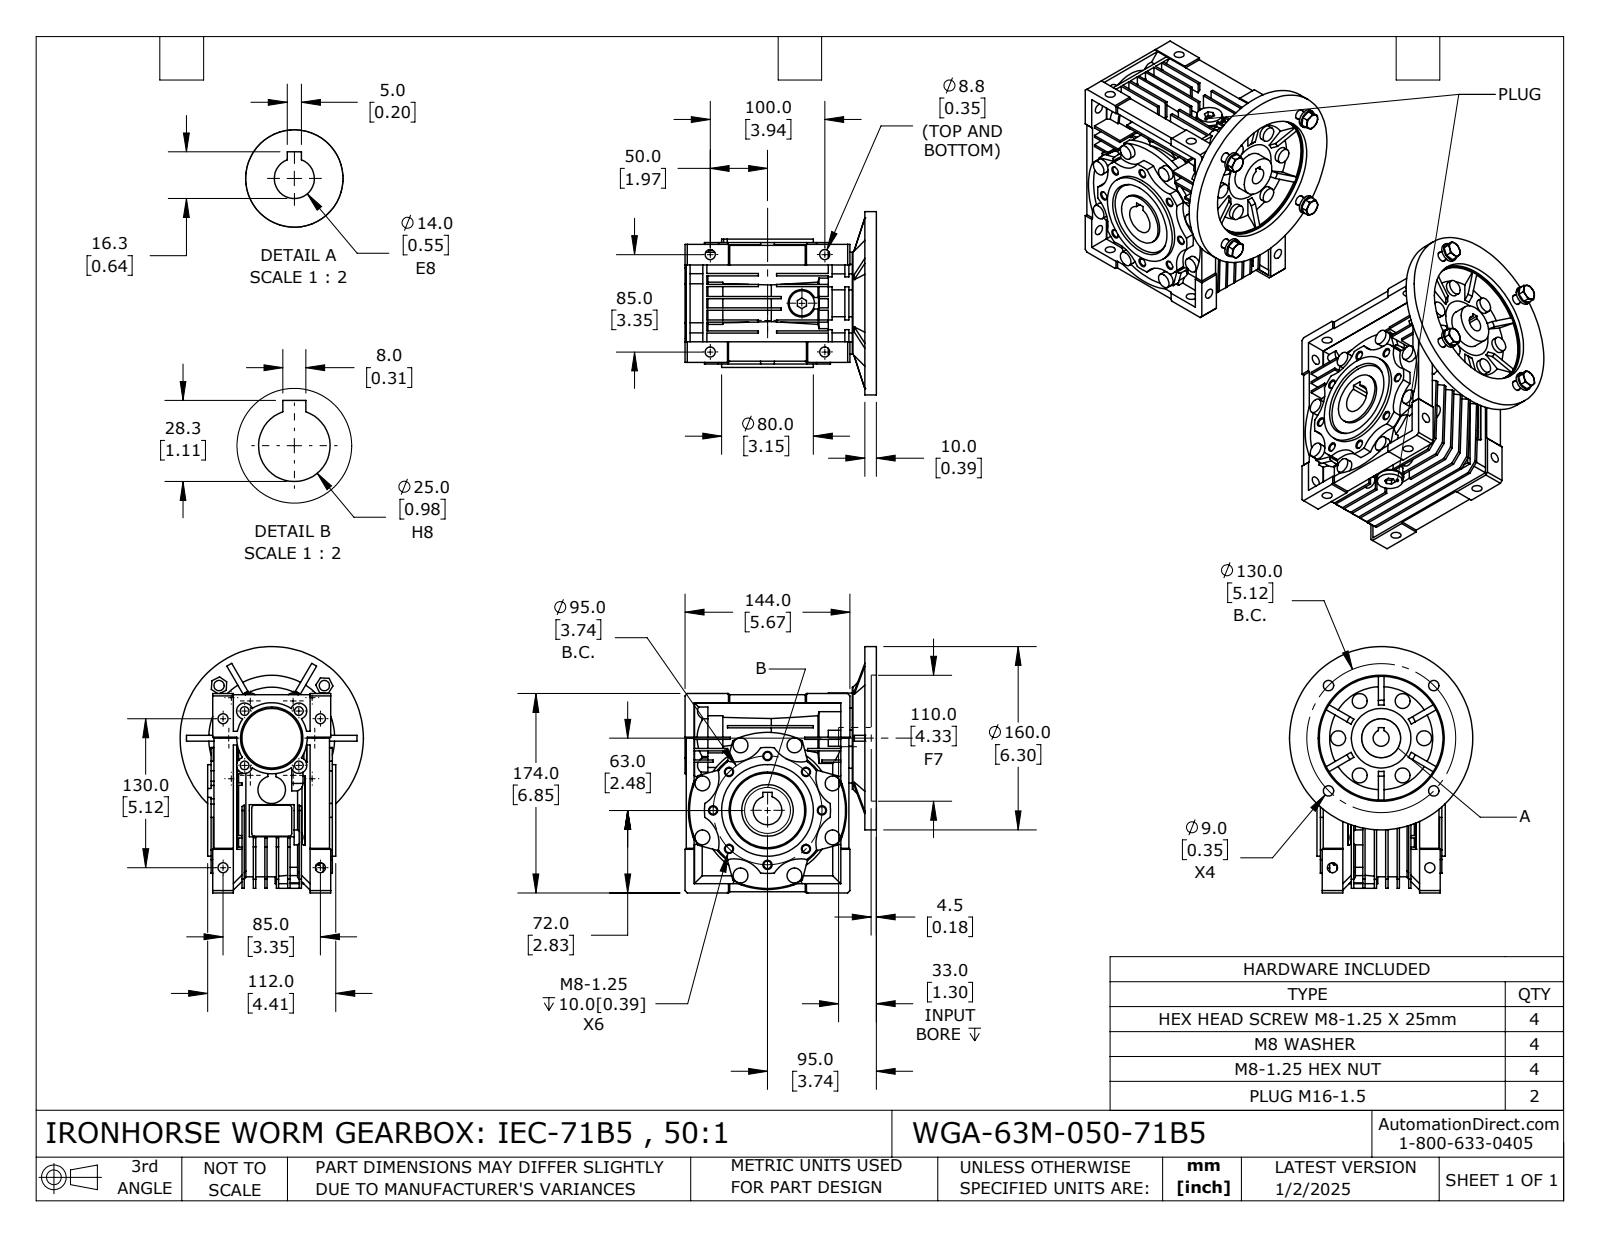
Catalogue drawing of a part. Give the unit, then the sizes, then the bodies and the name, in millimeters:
Units: millimetres
Overall size (bounding box): 215 × 182.98 × 160
Round holes (diameter × count): ⌀6.65 ×8, ⌀8.78 ×8, ⌀6.8 ×4, ⌀7.56 ×4, ⌀8 ×4, ⌀9 ×4, ⌀9.12 ×4, ⌀14.5 ×2, ⌀14 ×1, ⌀15 ×1, ⌀25 ×1, ⌀34 ×1
Round bosses / shafts (diameter × count): ⌀13 ×14, ⌀16 ×4, ⌀24 ×3, ⌀22 ×2, ⌀15.8 ×2, ⌀13.7 ×2, ⌀160 ×1, ⌀110 ×1
Partial cylindrical surfaces — rounded edges, fillets, slot ends (radius × count): R7 ×10, R27 ×8, R2.5 ×4, R8.35 ×1, R29.5 ×1, R30.5 ×1, R42 ×1, R58 ×1
Main face-to-face distances: 10, 8, 20, 2, 30, 12, 7, 18, 40, 1
Hole centre spacings: 36.36, 47.5, 67.18, 73.12, 87.77, 31.49, 33.5, 47.38
Volume: 1 919 000 mm³ · Surface area: 371 344 mm²
Bodies: 20 solids, 1516 faces (887 planar, 379 cylindrical, 250 other)
Part name (STEP PRODUCT): WGA-63M-050-71B5
STEP written by: SolidWorks 2024 (CONFIG_CONTROL_DESIGN)
